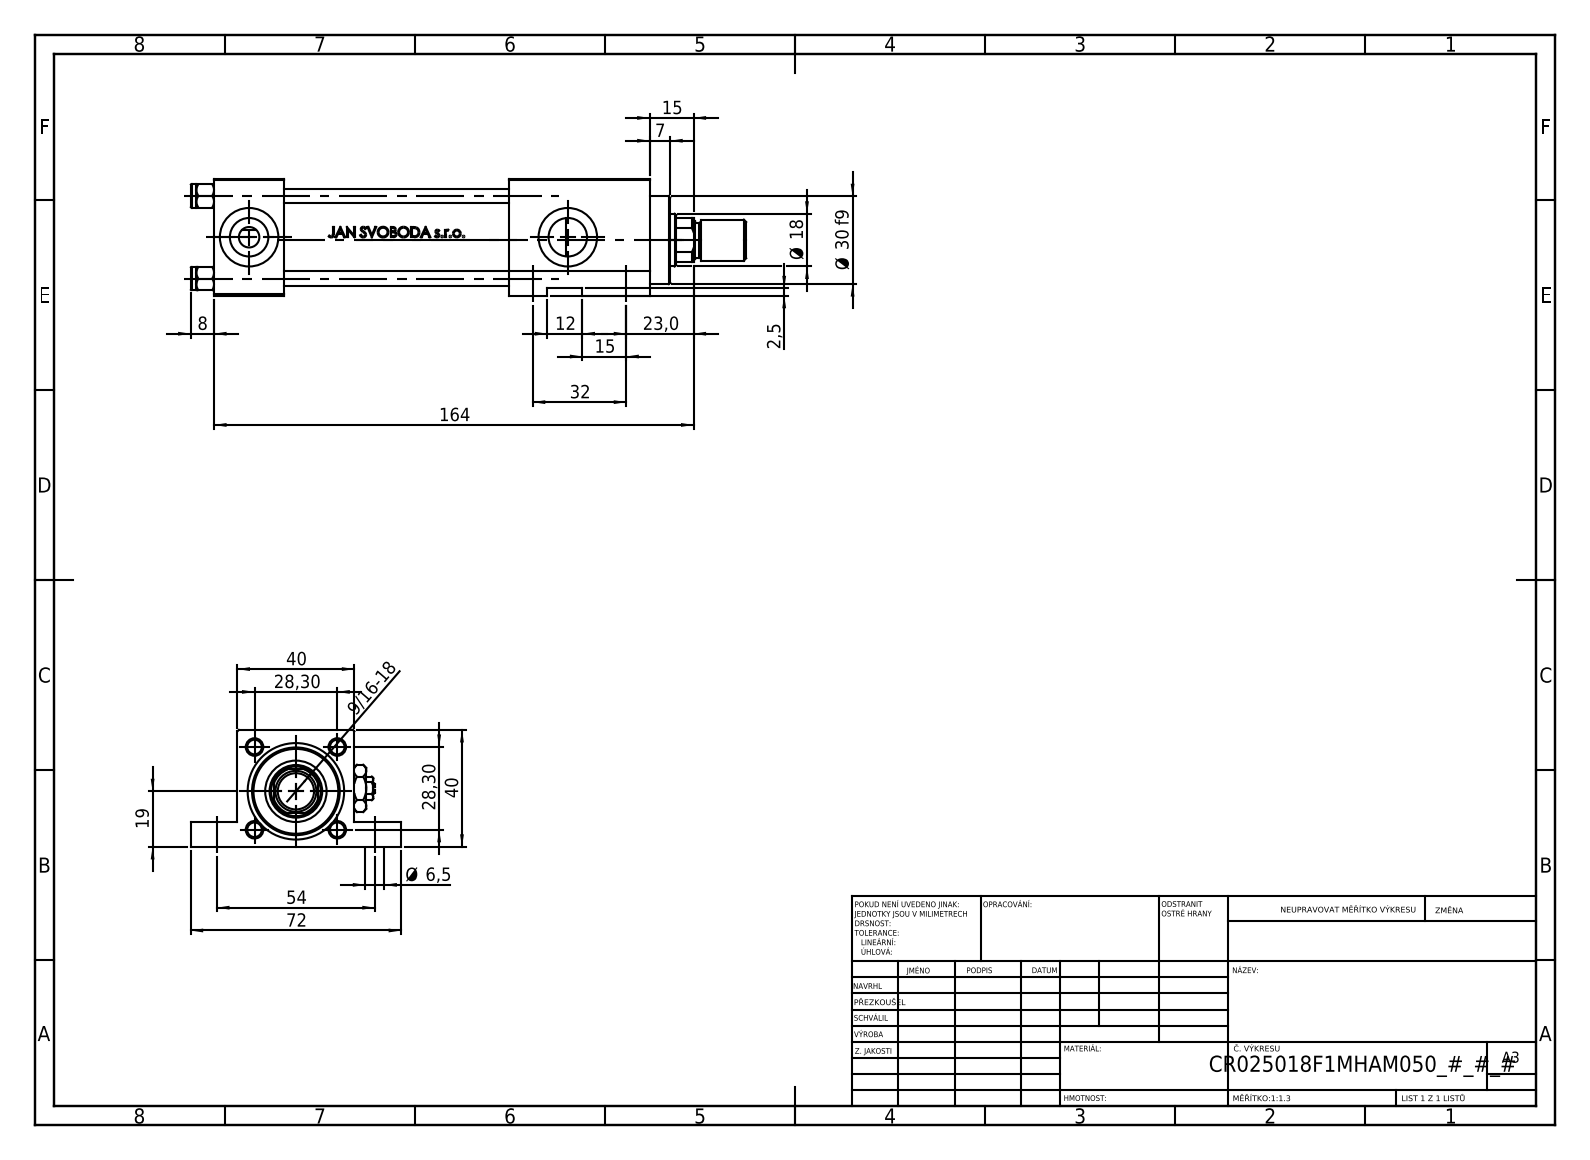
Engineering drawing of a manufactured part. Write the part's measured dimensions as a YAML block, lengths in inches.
part_name: "NUT_M5_F; Zatka_pro_OIL_PORT; V215CR_F_TYCINKA; ROD_END_AH (+3 more)"
step_written_by: "SolidWorks 2019 (CONFIG_CONTROL_DESIGN)"
units: inches
bodies: {solids: 13, faces: 1161, planar: 463, cylindrical: 132, other: 566}
overall_size: [7.48, 2.835, 1.575]
volume: 10.99
surface_area: 110.7
round_holes:
  - {diameter: 0.197, count: 4}
  - {diameter: 0.256, count: 4}
  - {diameter: 0.787, count: 4}
  - {diameter: 0.518, count: 3}
  - {diameter: 0.276, count: 2}
  - {diameter: 0.335, count: 1}
  - {diameter: 0.709, count: 1}
  - {diameter: 0.827, count: 1}
  - {diameter: 0.984, count: 1}
  - {diameter: 1.181, count: 1}
round_bosses_or_shafts:
  - {diameter: 0.315, count: 4}
  - {diameter: 1.22, count: 1}
  - {diameter: 0.551, count: 1}
  - {diameter: 0.472, count: 1}
partial_cylinders:
  - {radius: 0.335, count: 1}
face_to_face_distances: [1.575, 0.945, 0.335, 1.24, 3.976, 3.031, 0.236, 1.89, 2.205, 5.866]
hole_center_spacings: [1.114, 0.761, 0.816, 1.26, 1.576, 2.126, 2.471, 0.276]
